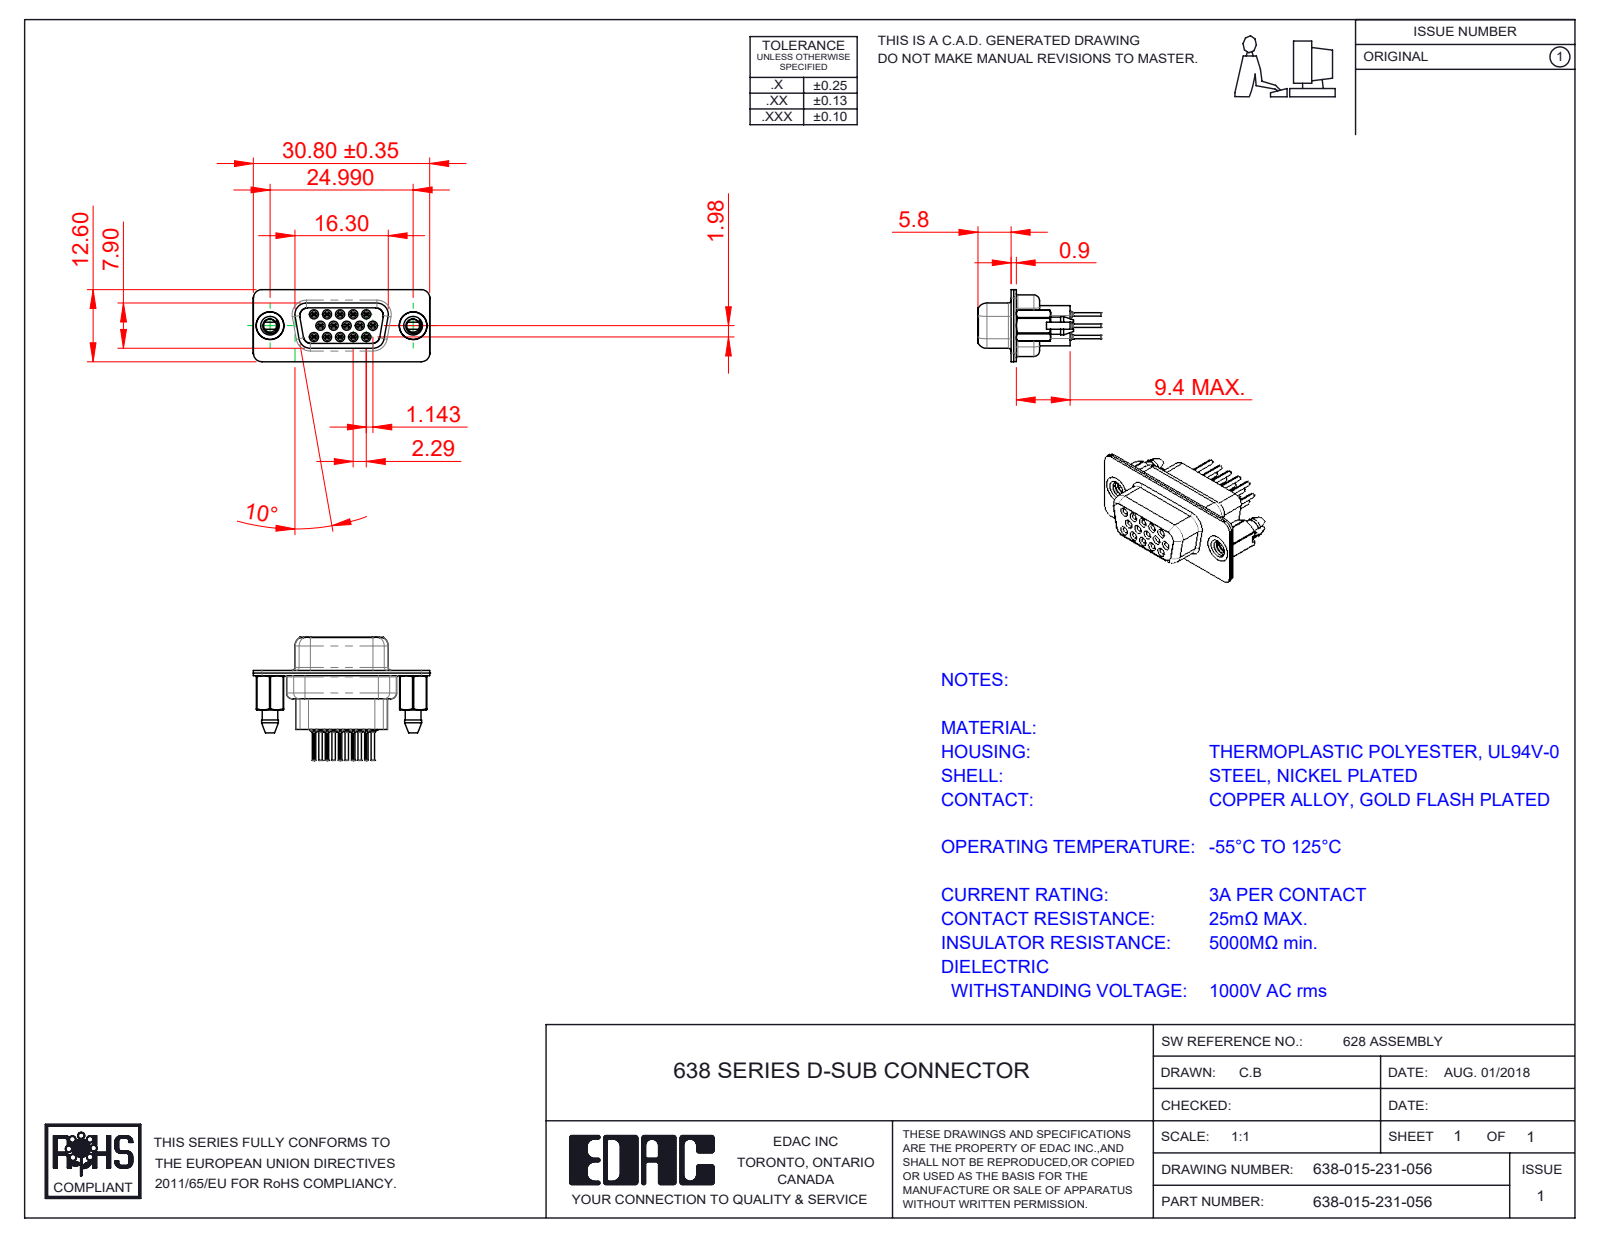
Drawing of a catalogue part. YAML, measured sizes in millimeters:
part_name: "638 Shell Rear_15 Contacts; 638 Contact Row 1_31; 638-015-231-056; 638 Housing_15 Contacts HP (+4 more)"
step_written_by: "SolidWorks 2020 (CONFIG_CONTROL_DESIGN)"
units: millimeters
bodies: {solids: 20, faces: 2198, planar: 564, cylindrical: 664, other: 970}
overall_size: [30.81, 21.5, 12.6]
volume: 1996
surface_area: 6817
round_holes:
  - {diameter: 0.2, count: 15}
  - {diameter: 0.8, count: 15}
  - {diameter: 1, count: 15}
  - {diameter: 1.1, count: 15}
  - {diameter: 1.6, count: 15}
  - {diameter: 1.7, count: 15}
  - {diameter: 1.8, count: 15}
  - {diameter: 2, count: 2}
  - {diameter: 2.26, count: 2}
  - {diameter: 4, count: 2}
  - {diameter: 4.05, count: 2}
  - {diameter: 4.85, count: 2}
round_bosses_or_shafts:
  - {diameter: 2, count: 15}
  - {diameter: 1.5, count: 15}
  - {diameter: 1.2, count: 15}
  - {diameter: 0.6, count: 15}
  - {diameter: 4.95, count: 2}
  - {diameter: 4.8, count: 2}
partial_cylinders:
  - {radius: 0.1, count: 30}
  - {radius: 1.5, count: 22}
  - {radius: 2, count: 12}
  - {radius: 0.28, count: 10}
  - {radius: 1.55, count: 8}
  - {radius: 1.35, count: 5}
  - {radius: 0.25, count: 4}
  - {radius: 0.5, count: 4}
face_to_face_distances: [0.45, 0.9, 0.4, 1.43, 6.6, 8.88, 7, 2.28, 5.8, 9.4]
hole_center_spacings: [3.96, 2.28, 4.57, 2.29, 6.05, 6.04, 6.86, 7.92]
